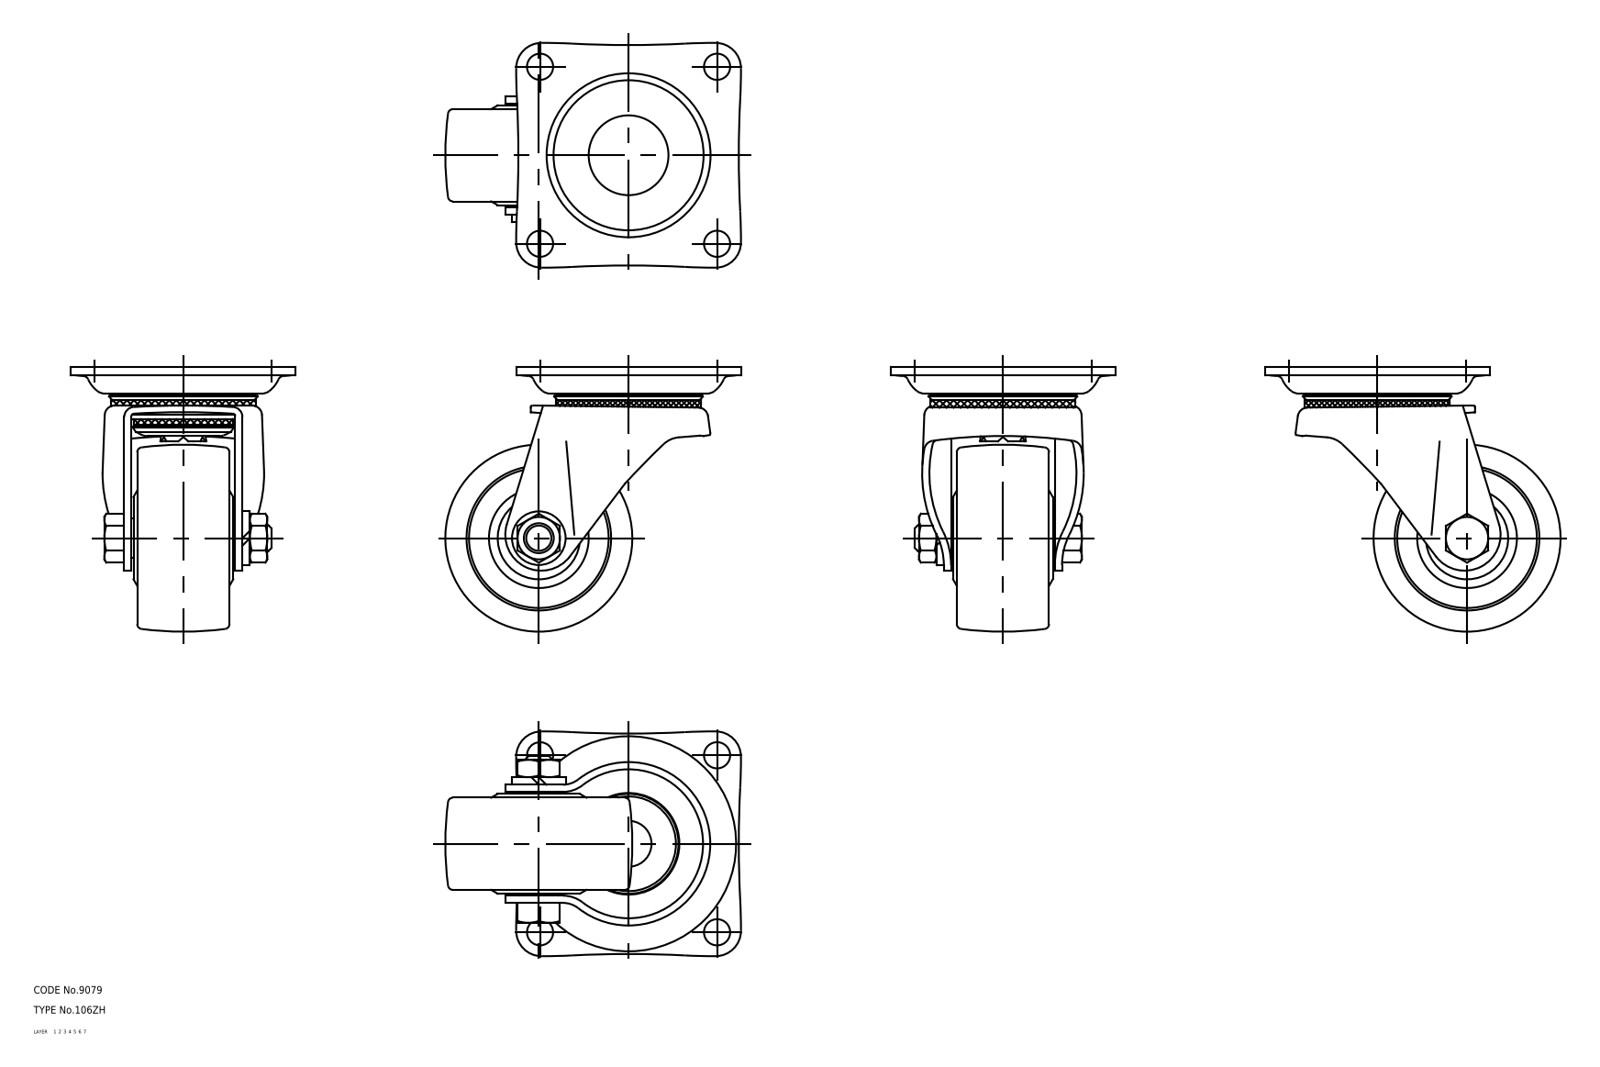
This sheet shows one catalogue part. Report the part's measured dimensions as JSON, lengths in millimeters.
{"part_name": "67130055; 67130068; 67130081; 67130094 (+1 more)", "step_written_by": "CADfix (AUTOMOTIVE_DESIGN)", "units": "millimeters", "bodies": {"solids": 5, "faces": 281, "planar": 0, "cylindrical": 0, "other": 281}, "overall_size": [118.51, 106, 90.02], "volume_mm3": 258206, "surface_area_mm2": 68871}
